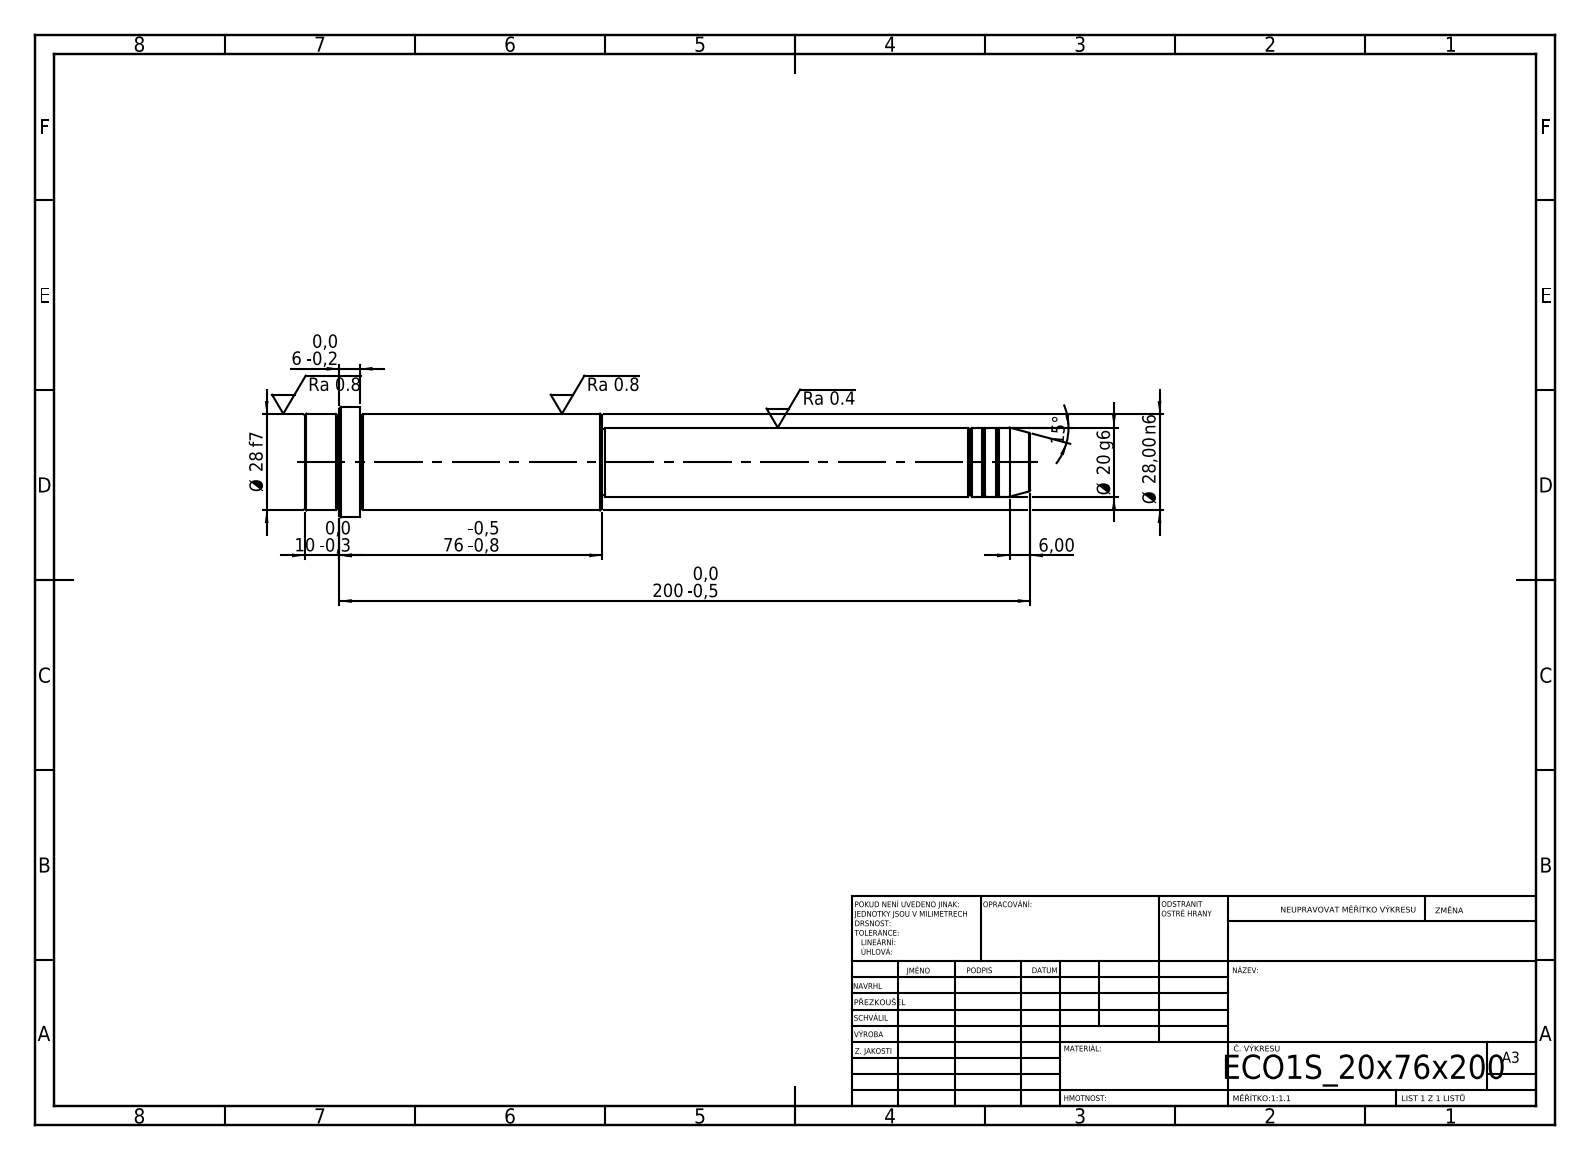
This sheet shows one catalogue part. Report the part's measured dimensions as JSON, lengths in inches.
{"step_written_by": "SolidWorks 2019 (CONFIG_CONTROL_DESIGN)", "units": "inches", "bodies": {"solids": 1, "faces": 52, "planar": 6, "cylindrical": 16, "other": 30}, "overall_size": [8.268, 1.26, 1.26], "volume_in3": 5.648, "surface_area_in2": 26.49, "round_bosses_or_shafts": [[1.26, 1], [1.102, 1], [0.787, 1], [0.748, 1]], "face_to_face_distances": [3.386, 4.882, 8.268, 7.638, 2.756, 0.63, 7.874, 2.992, 0.236, 0.394]}
